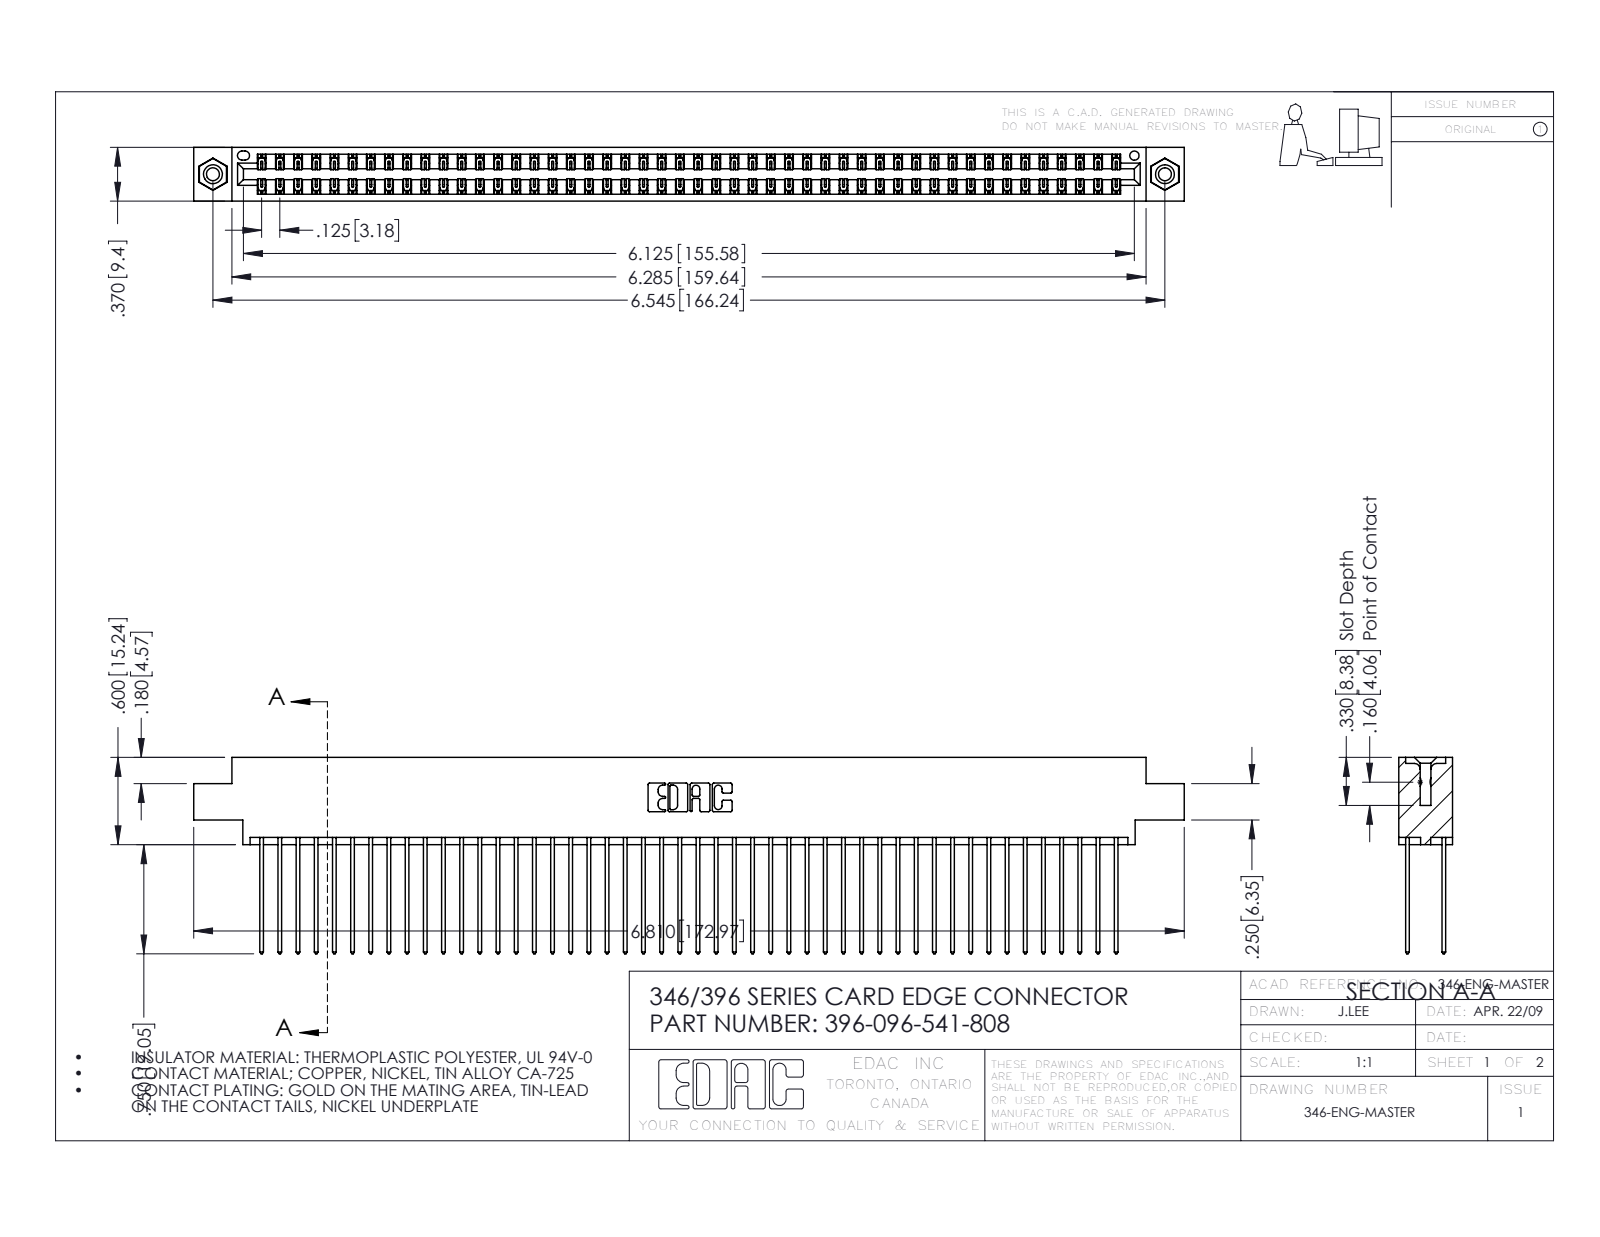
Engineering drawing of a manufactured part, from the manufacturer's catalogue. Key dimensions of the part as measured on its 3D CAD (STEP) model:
Part name (STEP PRODUCT): 345-292-001_345-293-141; 346 Part_0.170 Offset - 0.156 Dia-TI; 396-096-541-808; 345-250-001_345-250-003-102
STEP written by: SolidWorks 2016 (CONFIG_CONTROL_DESIGN)
Units: inches
Bodies: 99 solids, 5178 faces (3472 planar, 1690 cylindrical, 16 other)
Overall size (bounding box): 6.81 × 1.35 × 0.37
Volume: 1.056 in³ · Surface area: 41.42 in²
Round holes (diameter × count): ⌀0.089 ×2, ⌀0.125 ×2, ⌀0.156 ×2, ⌀0.064 ×1
Round bosses / shafts (diameter × count): ⌀0.155 ×2
Partial cylindrical surfaces — rounded edges, fillets, slot ends (radius × count): R0.006 ×144, R0.01 ×96, R0.01 ×22, R0.007 ×6, R0.031 ×6, R0.026 ×3, R0.014 ×2, R0.022 ×2
Main face-to-face distances: 0.048, 0.322, 0.25, 0.072, 0.298, 0.025, 0.37, 0.275, 0.225, 0.222
Hole centre spacings: 0.246, 6.336, 6.545
